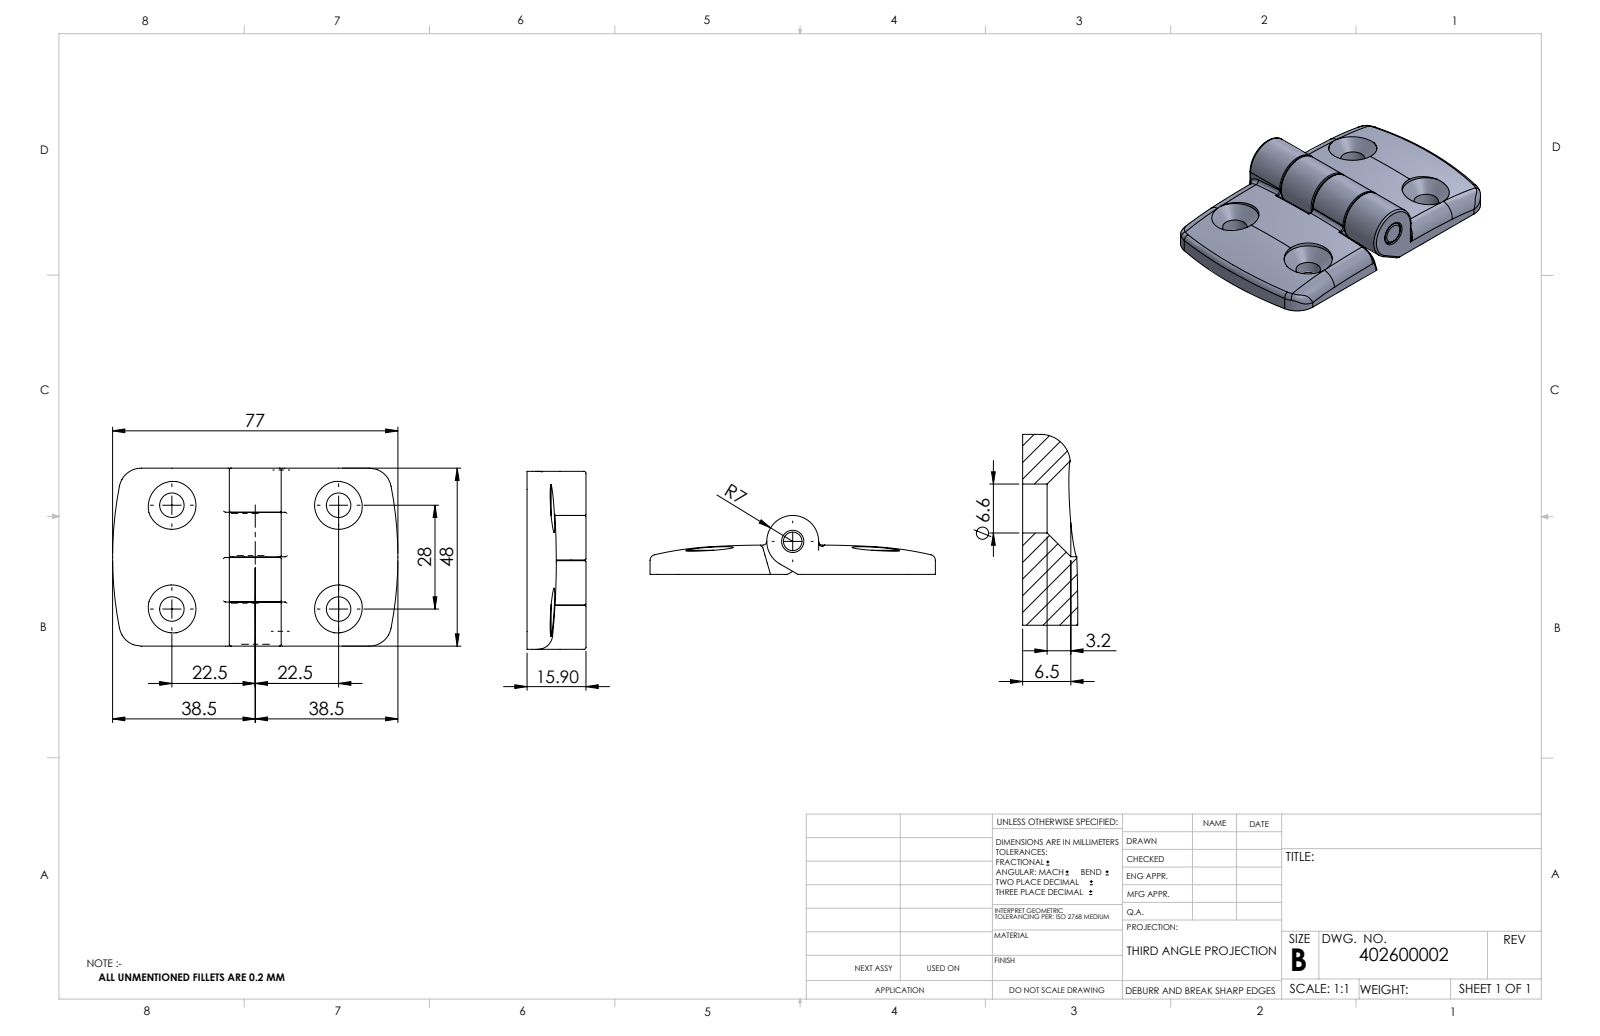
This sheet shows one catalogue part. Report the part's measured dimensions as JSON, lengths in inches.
{"part_name": "402600002_c_1", "step_written_by": "SolidWorks 2014 (CONFIG_CONTROL_DESIGN)", "units": "inches", "bodies": {"solids": 3, "faces": 171, "planar": 27, "cylindrical": 61, "other": 83}, "overall_size": [3.031, 1.89, 0.626], "volume_in3": 1.594, "surface_area_in2": 19.16, "round_holes": [[0.26, 4], [0.236, 1]], "round_bosses_or_shafts": [[0.551, 1], [0.244, 1]], "partial_cylinders_radius": [[0.012, 12], [0.02, 6], [0.236, 4], [0.256, 4], [0.157, 2], [3.937, 2]], "face_to_face_distances": [0.469, 1.421, 0.941, 0.949, 0.472, 0.48, 0.953, 1.89, 0.016, 0.453], "hole_center_spacings": [1.102, 1.772, 2.087]}
